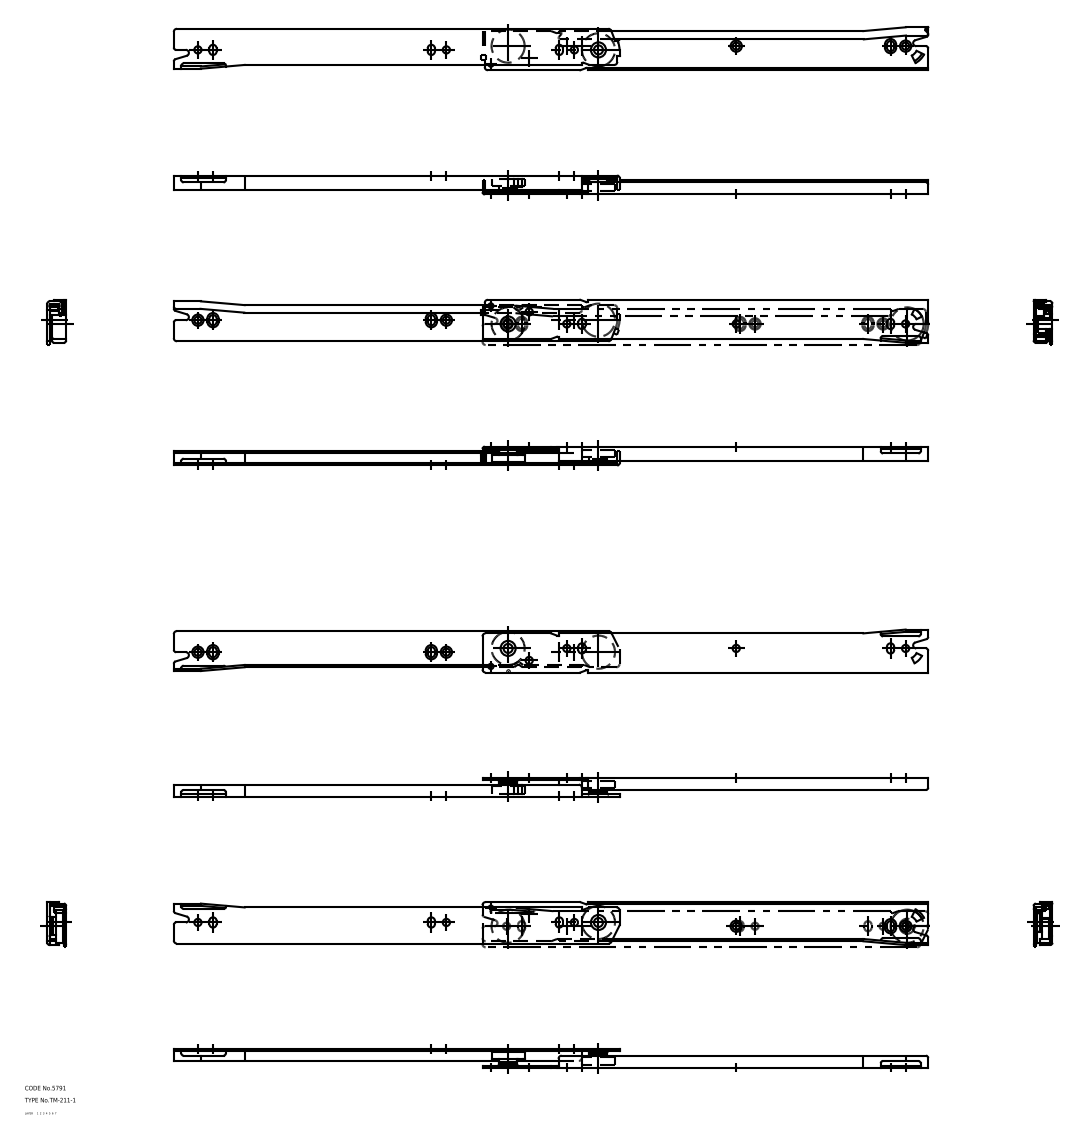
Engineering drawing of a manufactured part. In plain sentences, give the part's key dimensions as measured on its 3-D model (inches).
The part is named "roller; member_B; member_A; TM_211_1_1015_36". Its 3-D file was written by "CADfix (AUTOMOTIVE_DESIGN)". It is 4 solids with 177 faces: 0 planar, 0 cylindrical and 177 other. Overall it measures 19.724 by 1.122 by 0.492 inches. Its volume is 1.989 cubic inches and its surface area 66.18 square inches.
